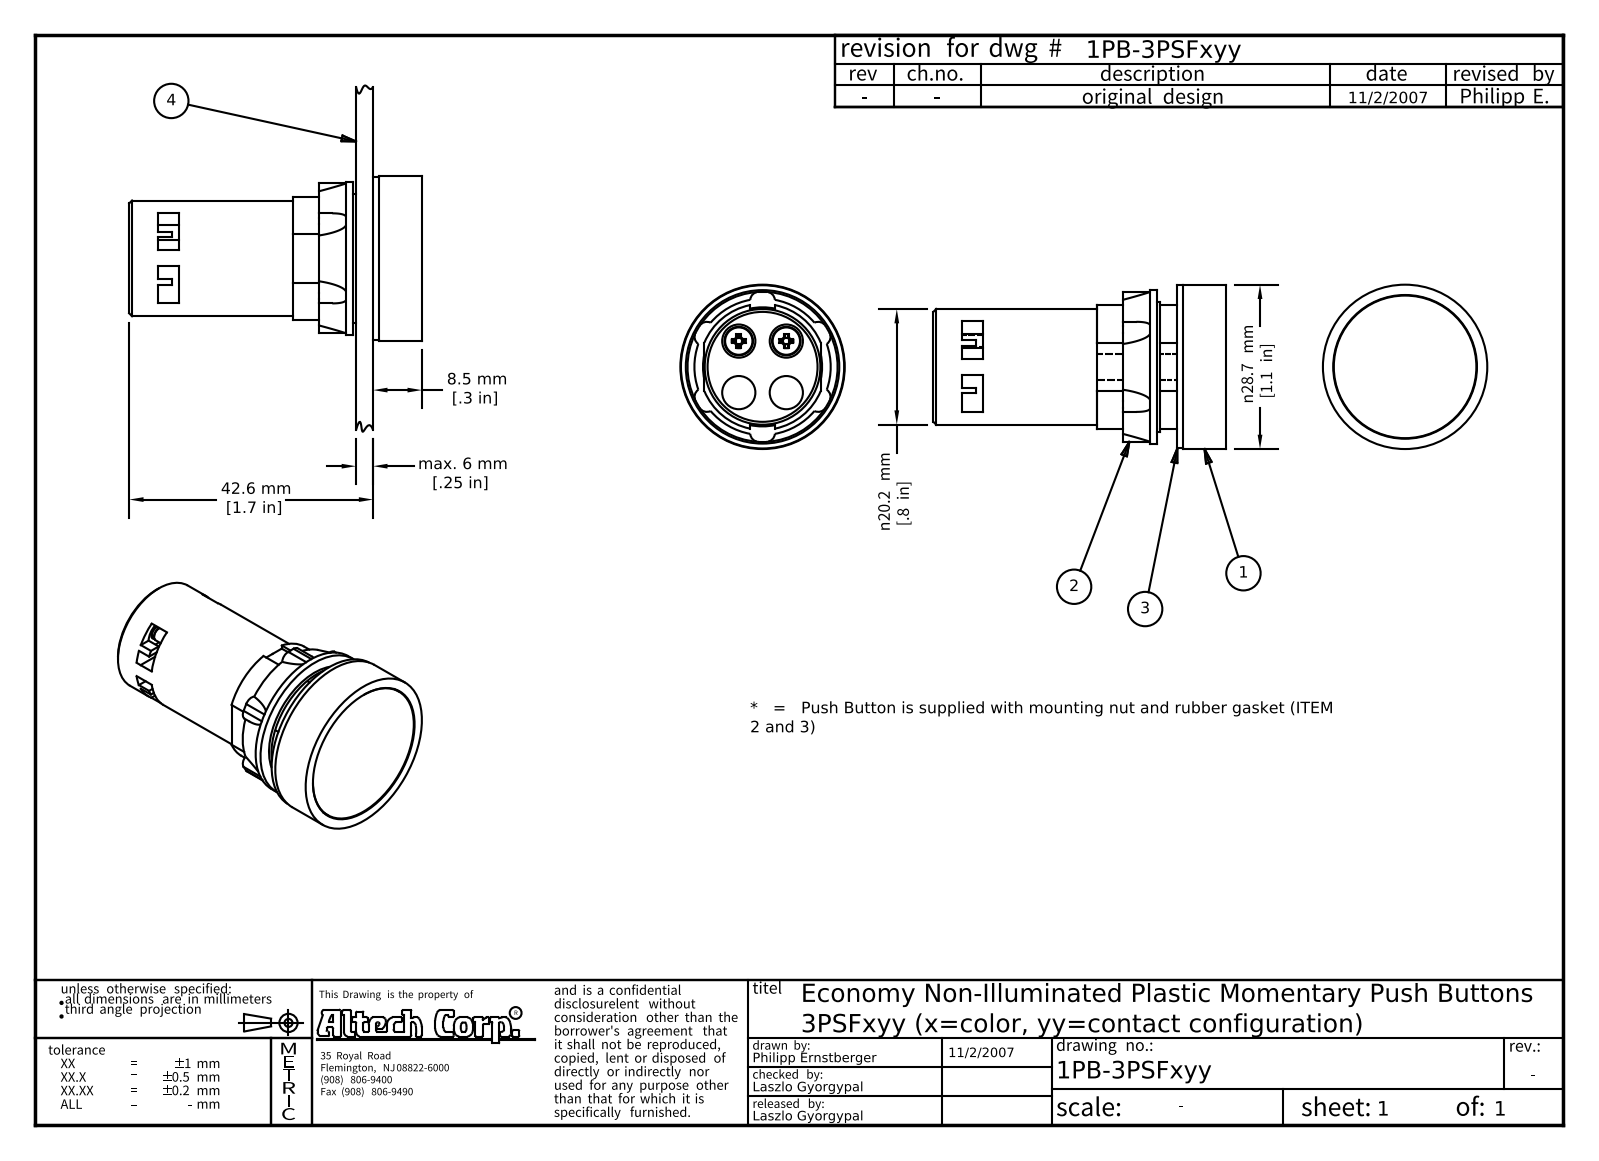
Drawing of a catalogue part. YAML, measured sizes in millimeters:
part_name: "3PSFxyy; 3PSFxxx; P2MN; panel_long (+1 more)"
step_written_by: "Autodesk Inventor 2008 (AUTOMOTIVE_DESIGN)"
units: millimeters
bodies: {solids: 5, faces: 202, planar: 122, cylindrical: 37, other: 43}
overall_size: [60.45, 51.1, 45]
volume: 26056
surface_area: 13871
round_holes:
  - {diameter: 5.8, count: 4}
  - {diameter: 20.8, count: 1}
  - {diameter: 22.5, count: 1}
  - {diameter: 25.1, count: 1}
round_bosses_or_shafts:
  - {diameter: 2.5, count: 2}
  - {diameter: 2.27, count: 2}
  - {diameter: 28.7, count: 1}
  - {diameter: 28.5, count: 1}
  - {diameter: 26.8, count: 1}
  - {diameter: 24.9, count: 1}
  - {diameter: 22.6, count: 1}
  - {diameter: 20.2, count: 1}
partial_cylinders:
  - {radius: 1.5, count: 12}
  - {radius: 11, count: 1}
face_to_face_distances: [3, 11.4, 8.4, 5, 12.35, 32.65, 39.6, 42.6, 51, 45]
hole_center_spacings: [6.12, 8.3, 9, 12.24]
